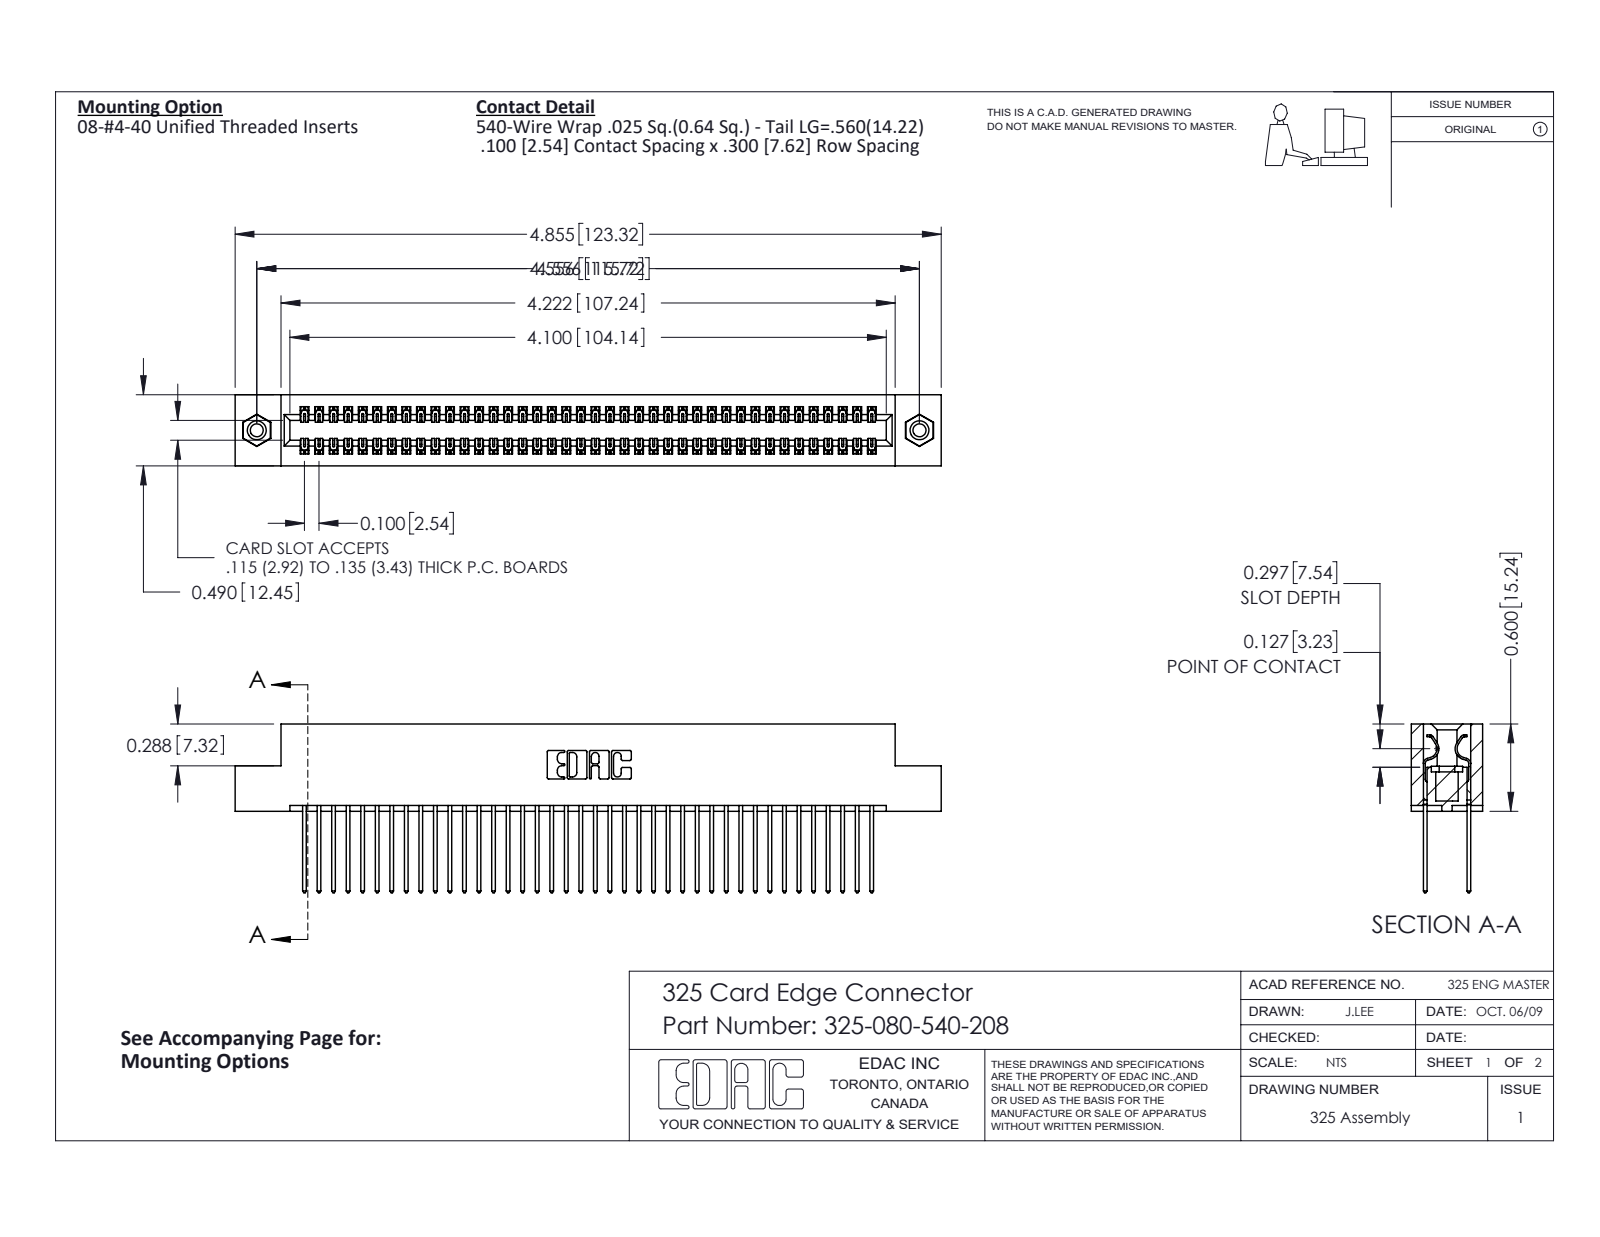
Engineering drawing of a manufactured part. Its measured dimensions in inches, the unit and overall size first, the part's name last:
Units: inches
Overall size (bounding box): 4.855 × 1.16 × 0.49
Round holes (diameter × count): ⌀0.089 ×2, ⌀0.125 ×2, ⌀0.16 ×2
Round bosses / shafts (diameter × count): ⌀0.155 ×2
Partial cylindrical surfaces — rounded edges, fillets, slot ends (radius × count): R0.006 ×120, R0.01 ×80, R0.01 ×22, R0.007 ×6, R0.031 ×6, R0.026 ×3, R0.014 ×2, R0.022 ×2
Main face-to-face distances: 0.083, 0.407, 0.3, 0.107, 0.383, 0.025, 0.49, 0.325, 0.275, 0.56
Hole centre spacings: 4.556
Volume: 0.989 in³ · Surface area: 32.58 in²
Bodies: 83 solids, 4334 faces (2982 planar, 1336 cylindrical, 16 other)
Part name (STEP PRODUCT): 325-080-540-208; 345-250-001_345-250-003-102; 325-292-001_325-293-140; 325 Part_TI
STEP written by: SolidWorks 2016 (CONFIG_CONTROL_DESIGN)
